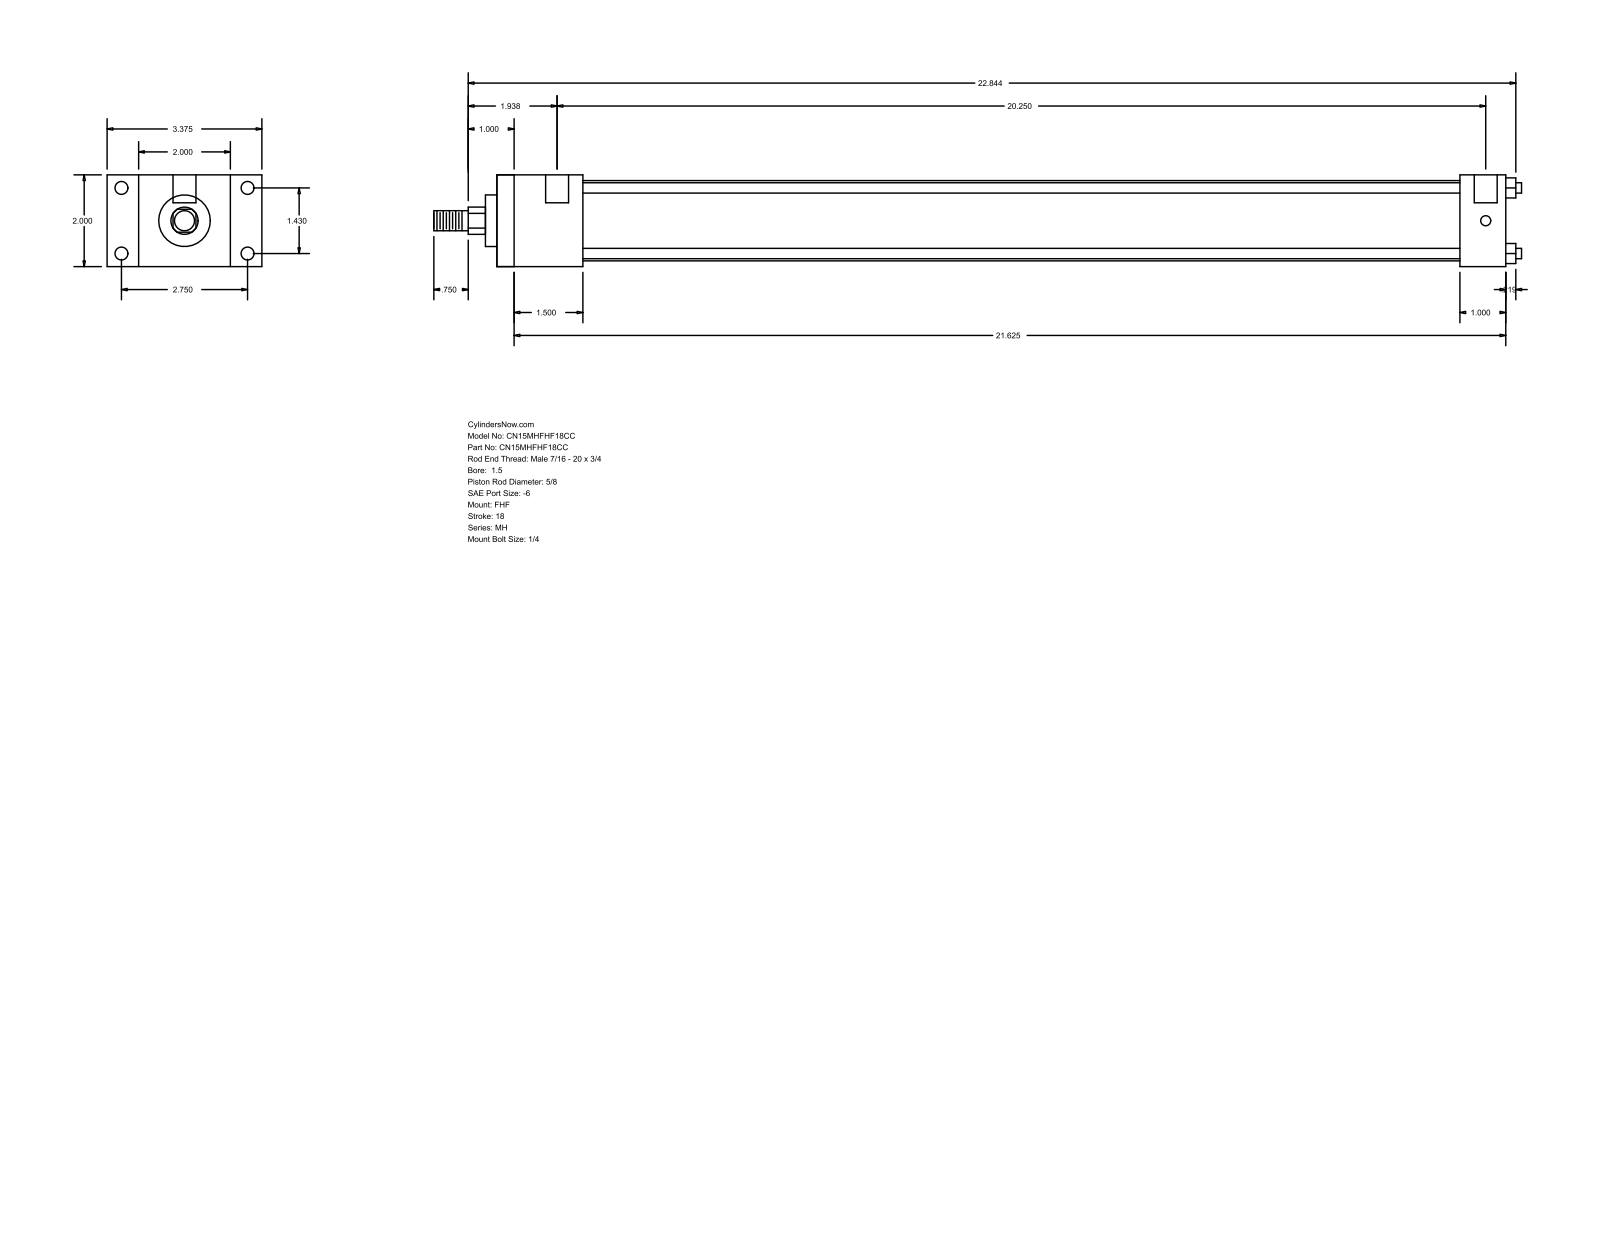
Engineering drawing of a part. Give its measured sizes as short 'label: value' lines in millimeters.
name: MH_FHF__0150_0.625
written by: GSSL Pune (CONFIG_CONTROL_DESIGN)
unit: mm
bodies: 0 solids, 88 faces (60 planar, 28 cylindrical, 0 other)
size: 602.46 × 85.72 × 50.8
holes: 4× ⌀5.56, 4× ⌀7.14, 2× ⌀12.7
bosses: 4× ⌀5.71, 1× ⌀44.45, 1× ⌀28.57, 1× ⌀15.88, 1× ⌀11.11
rounds: 1× R7.54
face distances: 50.8, 17.46, 68.26, 47.62, 85.72, 558.79, 511.17, 25.4, 533.39, 485.77
hole spacings: 36.32, 69.84, 78.72, 517.52, 3.17, 514.35
